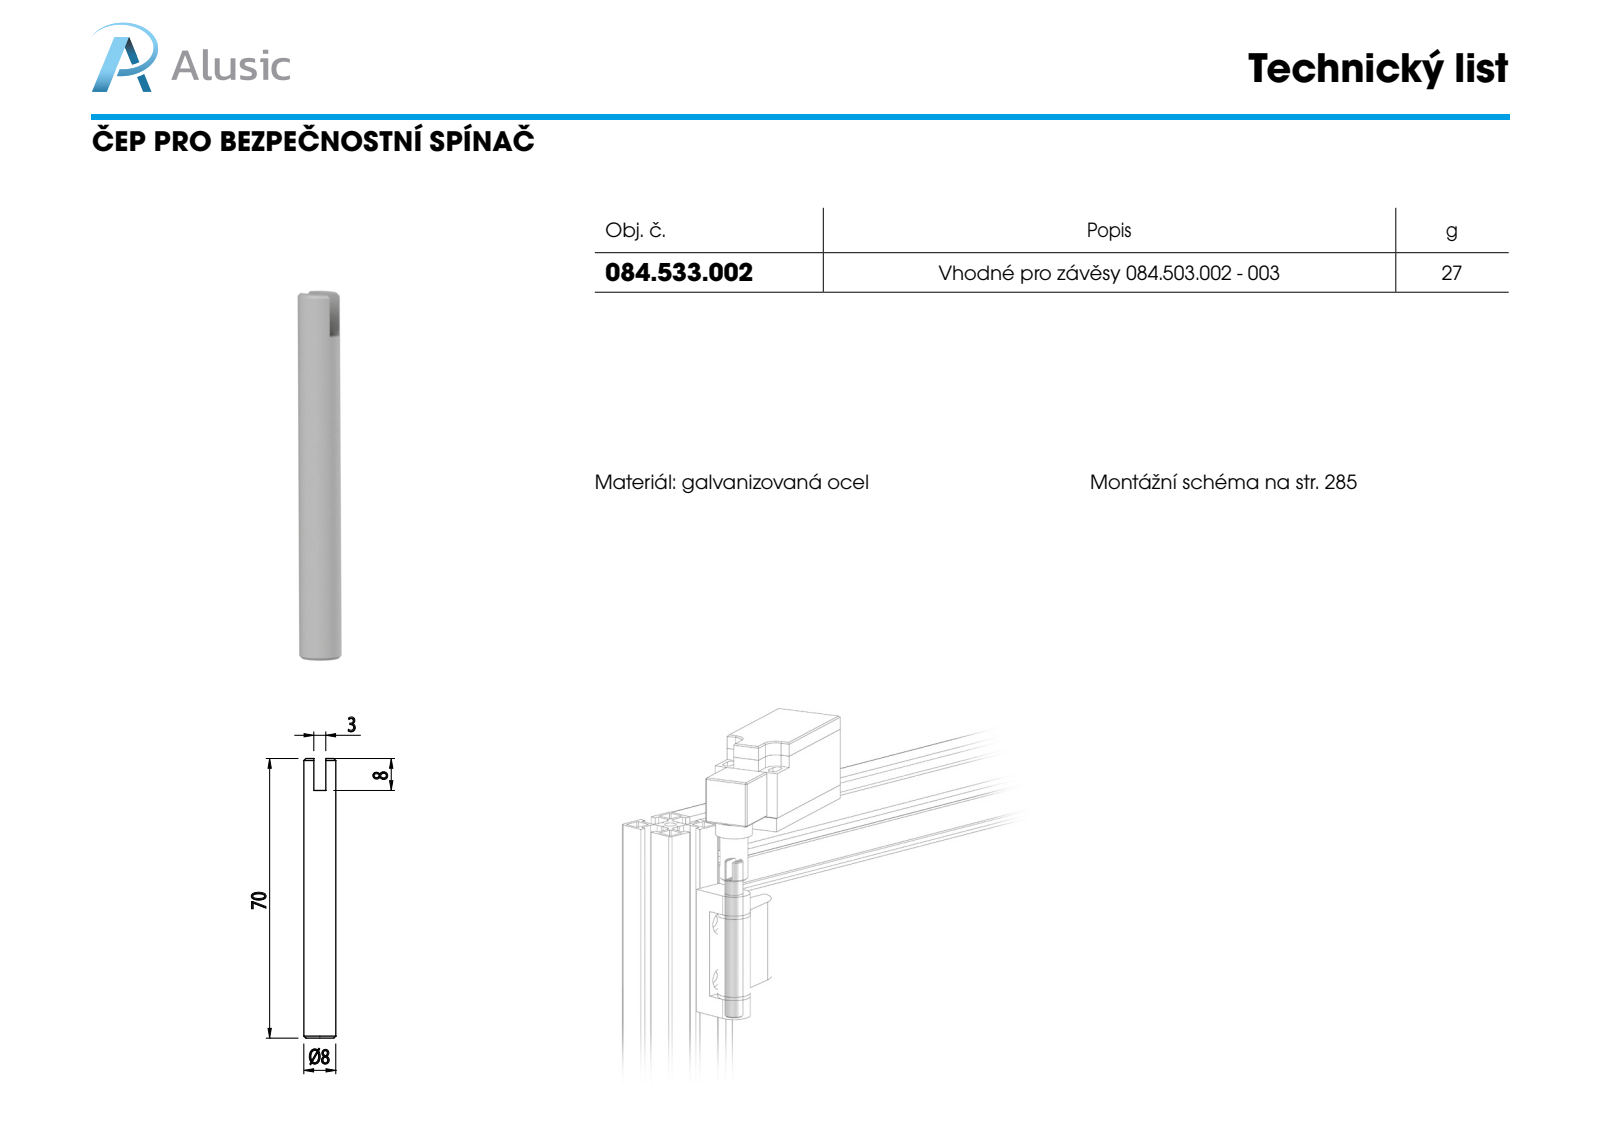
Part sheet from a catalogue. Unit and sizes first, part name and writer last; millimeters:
Units: millimetres
Overall size (bounding box): 70 × 8 × 8
Round bosses / shafts (diameter × count): ⌀8 ×1
Main face-to-face distances: 3, 62, 70, 8
Volume: 3 326 mm³ · Surface area: 1 915 mm²
Bodies: 1 solid, 12 faces (6 planar, 2 cylindrical, 4 other)
Part name (STEP PRODUCT): 084.533.002
STEP written by: SolidWorks 2011 (CONFIG_CONTROL_DESIGN)
